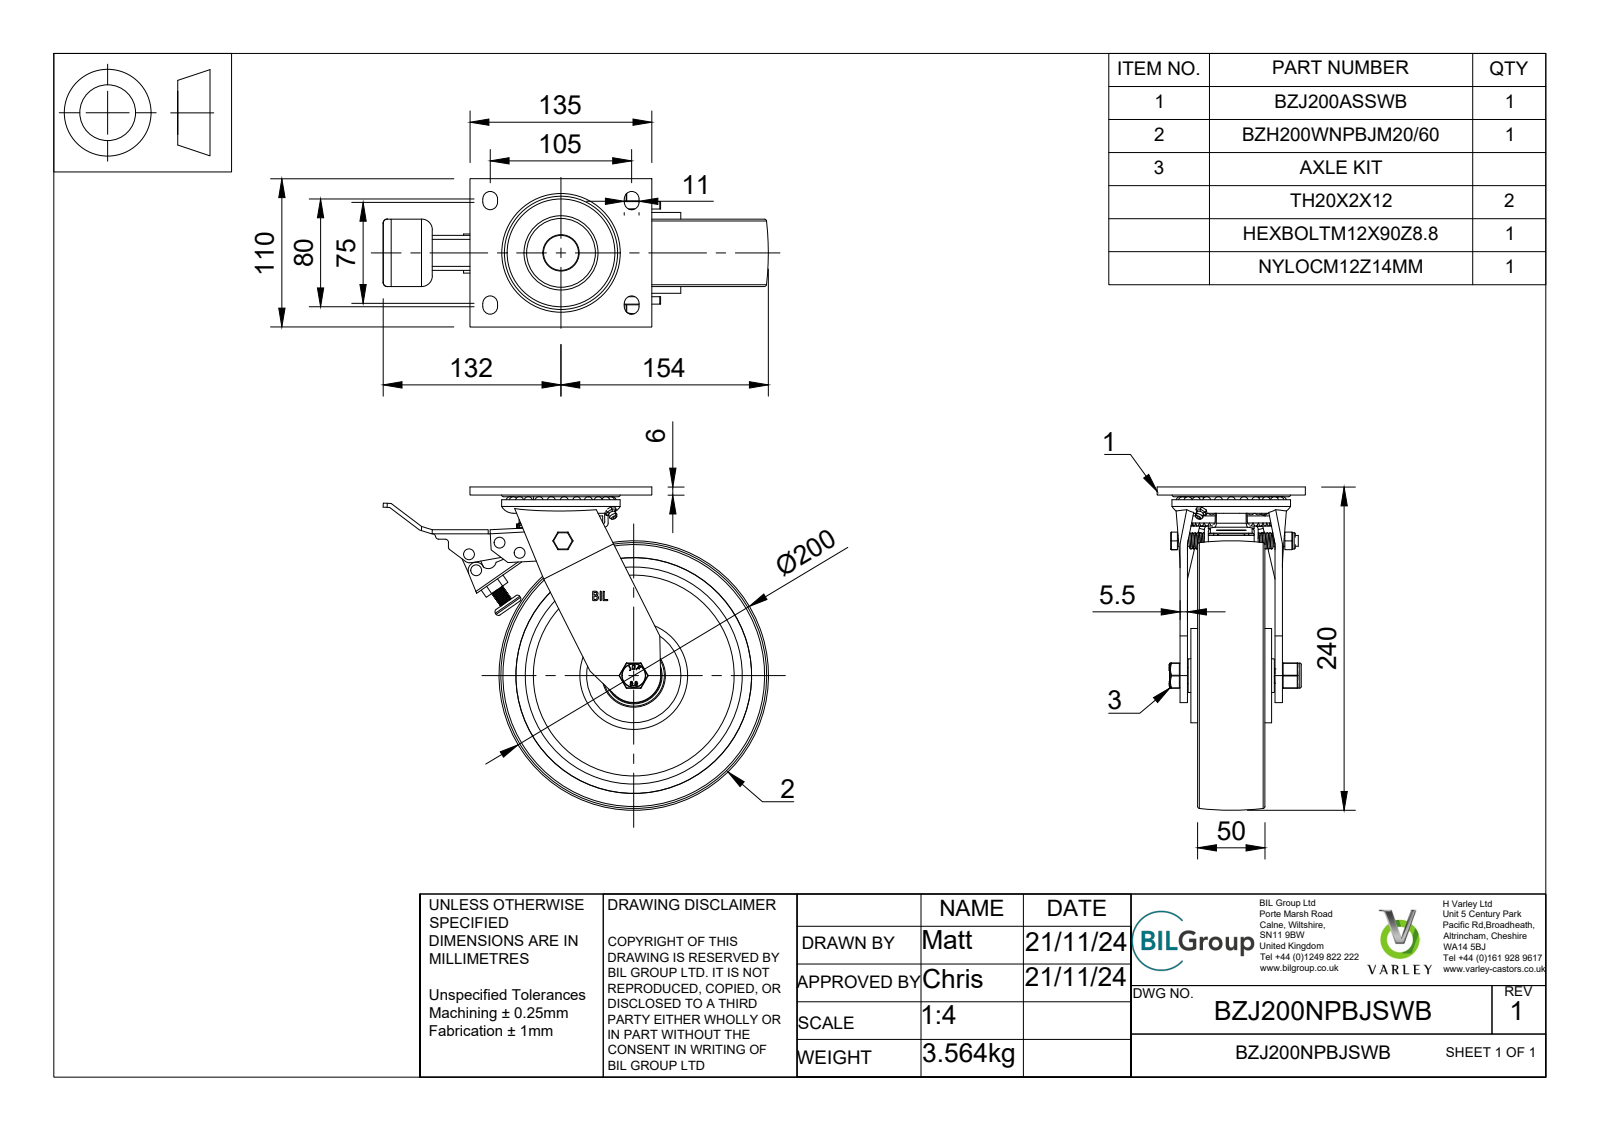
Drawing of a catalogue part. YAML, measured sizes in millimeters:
part_name: "BZJ200NPBJSWB v3; BZJ200ASSWB v1; FABRICATED STEEL TOP PLATE; FABRICATED STEEL TOP PLATE Geometry (+6 more)"
step_written_by: "Autodesk Translation Framework v13.20.0.188 (AP242_MANAGED_MODEL_BASED_3D_ENGINEERING_MIM_LF)"
units: millimeters
bodies: {solids: 98, faces: 1885, planar: 823, cylindrical: 316, other: 746}
overall_size: [286, 240, 110]
volume: 1143000
surface_area: 372802
round_holes:
  - {diameter: 4, count: 4}
  - {diameter: 6, count: 4}
  - {diameter: 8, count: 2}
  - {diameter: 10, count: 1}
  - {diameter: 12, count: 1}
  - {diameter: 12.2, count: 1}
  - {diameter: 13, count: 1}
  - {diameter: 14, count: 1}
  - {diameter: 20, count: 1}
  - {diameter: 28.5, count: 1}
  - {diameter: 30, count: 1}
  - {diameter: 30.8, count: 1}
round_bosses_or_shafts:
  - {diameter: 8, count: 5}
  - {diameter: 12, count: 2}
  - {diameter: 88, count: 1}
  - {diameter: 70, count: 1}
  - {diameter: 69, count: 1}
  - {diameter: 62, count: 1}
  - {diameter: 40.8, count: 1}
  - {diameter: 40.62, count: 1}
partial_cylinders:
  - {radius: 0.5, count: 30}
  - {radius: 1.5, count: 8}
  - {radius: 5.5, count: 8}
  - {radius: 3, count: 7}
  - {radius: 0.47, count: 4}
  - {radius: 0.9, count: 4}
  - {radius: 2.5, count: 3}
  - {radius: 6, count: 3}
face_to_face_distances: [6, 28, 22, 13, 35, 41, 5.5, 7.5, 50, 63]
hole_center_spacings: [1.5, 13, 16.69, 24.27, 26.87, 31.92, 33.36, 34.82]
